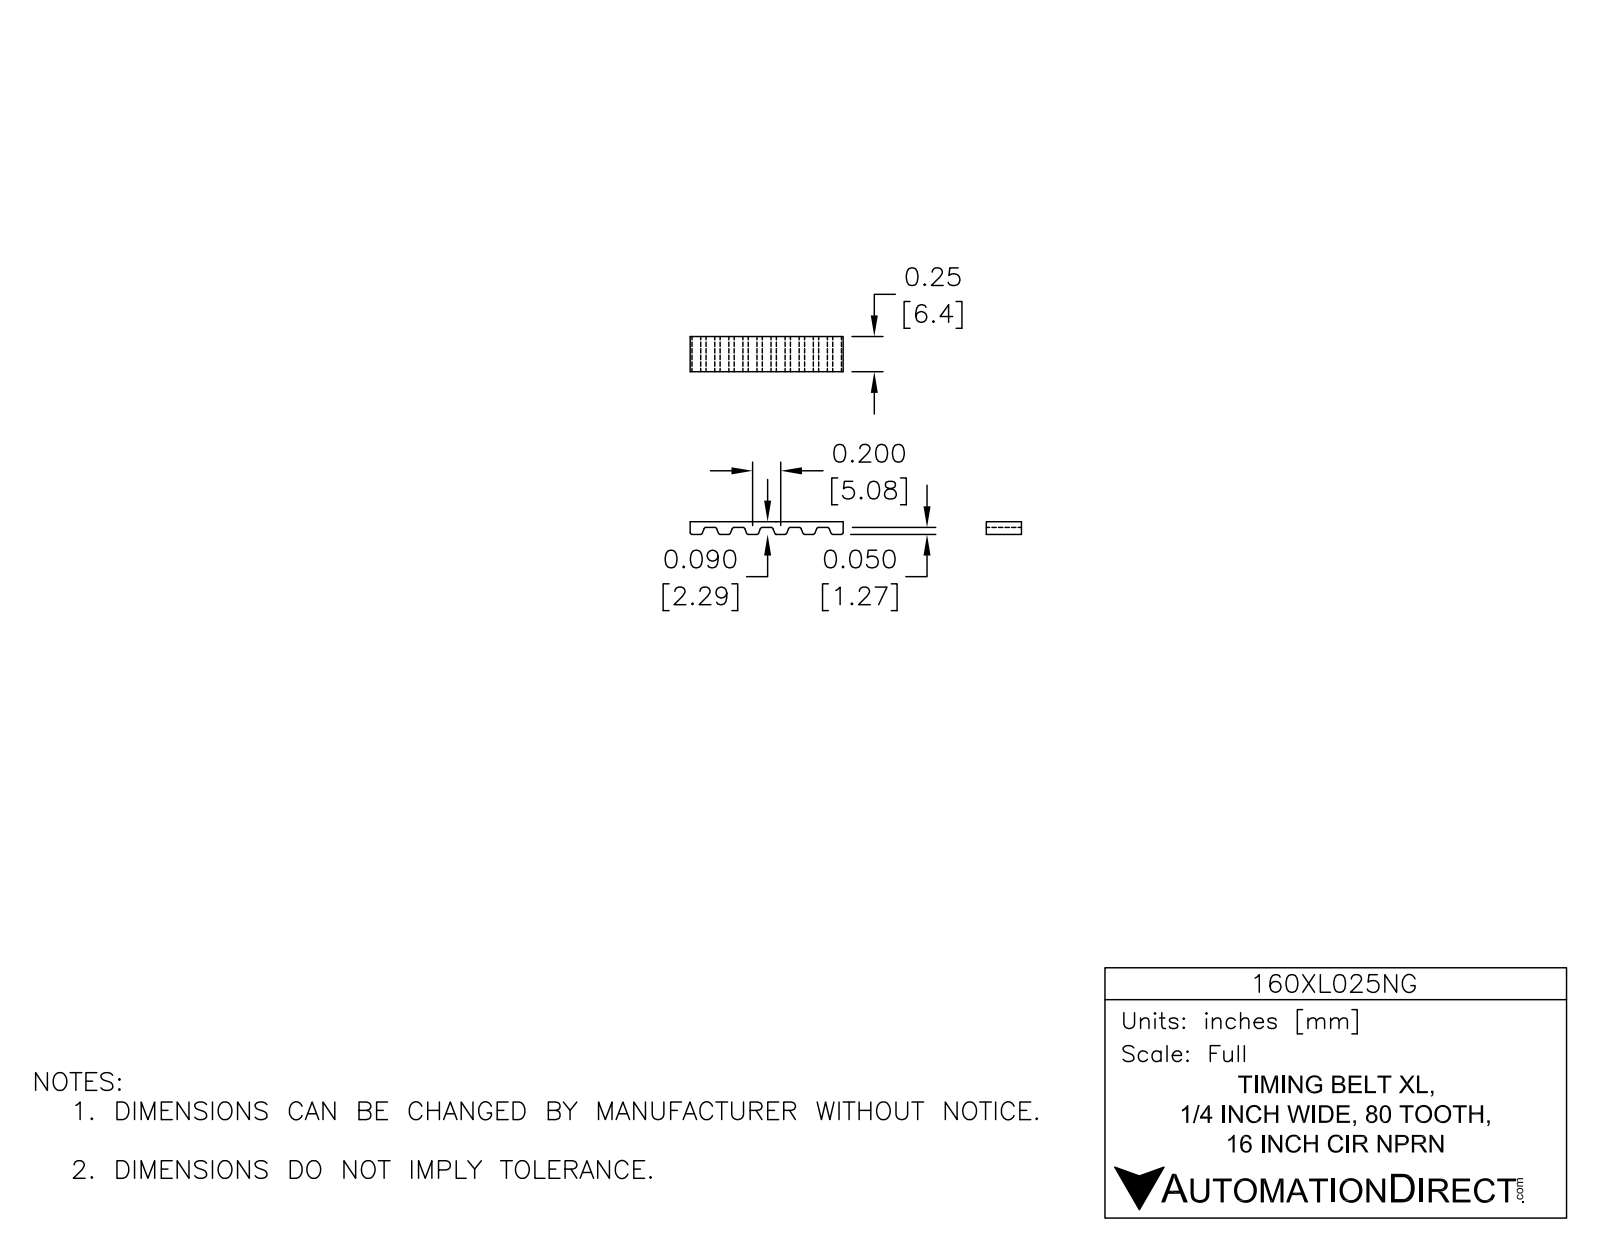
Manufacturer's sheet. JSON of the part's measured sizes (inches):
{"part_name": "160XL025NG", "step_written_by": "SolidWorks 2014 (AUTOMOTIVE_DESIGN)", "units": "inches", "bodies": {"solids": 1, "faces": 678, "planar": 280, "cylindrical": 398, "other": 0}, "overall_size": [6.288, 3, 0.25], "volume_in3": 0.217, "surface_area_in2": 10.78, "partial_cylinders_radius": [[0.015, 320], [1.46, 2], [1.5, 2]], "face_to_face_distances": [0.25, 3, 0.04, 2.96, 2.92, 0.178, 0.357, 0.535, 0.713, 0.892]}
